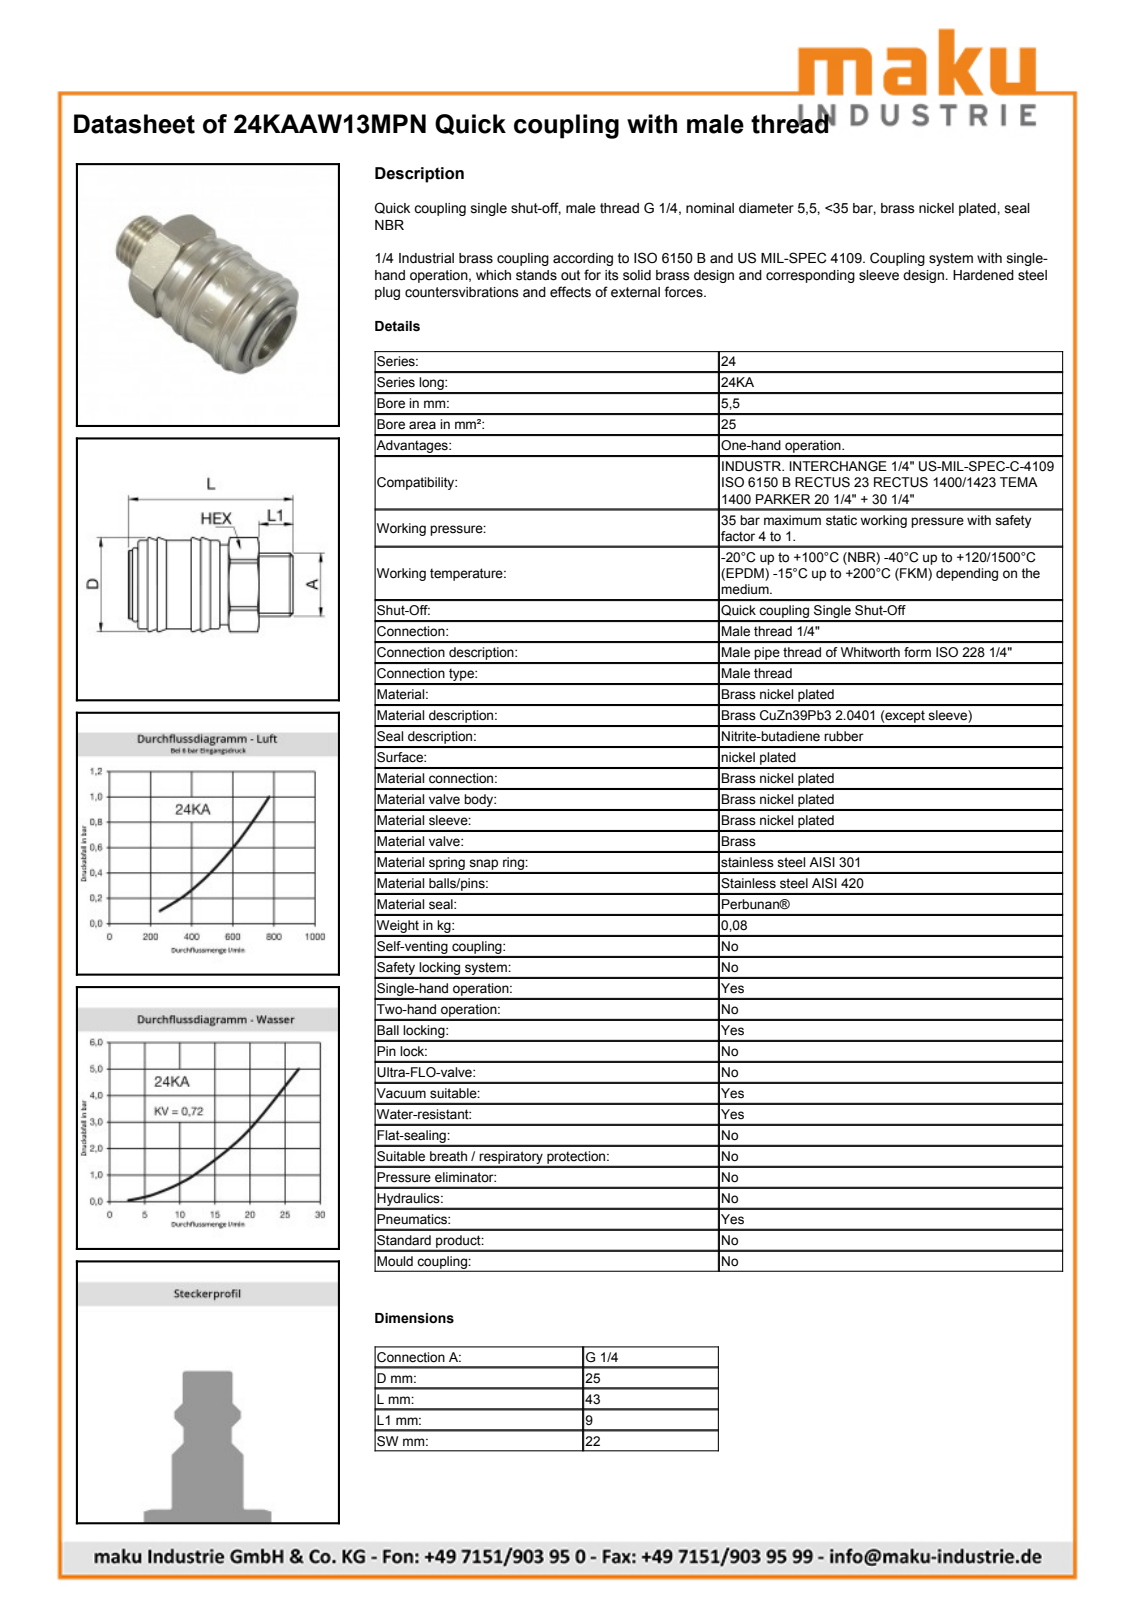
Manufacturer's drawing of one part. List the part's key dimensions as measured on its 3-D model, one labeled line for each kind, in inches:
Part name (STEP PRODUCT): D108576
STEP written by: Autodesk Inventor 2013 (AUTOMOTIVE_DESIGN)
Units: inches
Bodies: 3 solids, 470 faces (168 planar, 58 cylindrical, 244 other)
Overall size (bounding box): 1.697 × 0.976 × 0.976
Volume: 0.816 in³ · Surface area: 11.3 in²
Round holes (diameter × count): ⌀0.634 ×1, ⌀0.669 ×1, ⌀0.831 ×1
Round bosses / shafts (diameter × count): ⌀0.917 ×1, ⌀0.827 ×1, ⌀0.709 ×1, ⌀0.657 ×1, ⌀0.628 ×1, ⌀0.589 ×1, ⌀0.518 ×1
Partial cylindrical surfaces — rounded edges, fillets, slot ends (radius × count): R0.294 ×1, R0.455 ×1, R0.488 ×1
Main face-to-face distances: 0.866, 1.238, 0.104, 1.343, 0.906, 0.354, 1.697, 1.593, 0.437, 0.801
